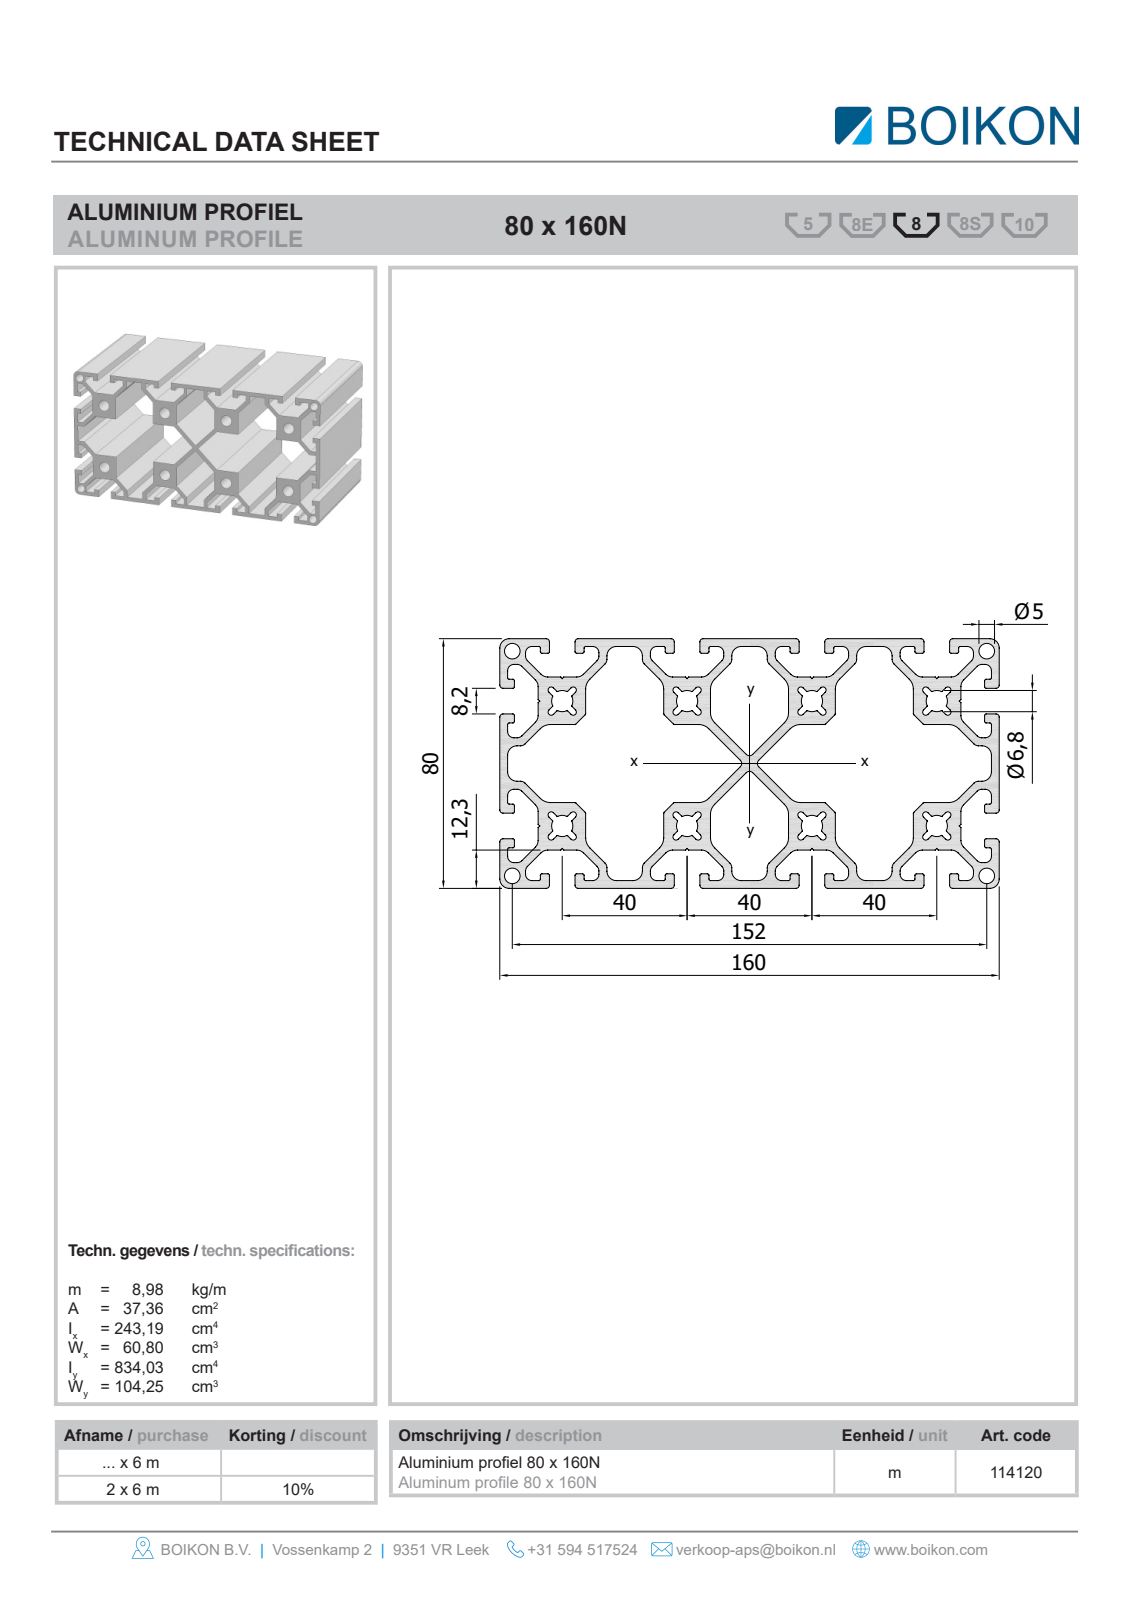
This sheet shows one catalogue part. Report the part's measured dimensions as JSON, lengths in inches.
{"part_name": "Root; 11412080x160NBOIKON0", "step_written_by": "HiCAD 2013 1802.4 Build 509 (AUTOMOTIVE_DESIGN)", "units": "inches", "bodies": {"solids": 1, "faces": 258, "planar": 242, "cylindrical": 16, "other": 0}, "overall_size": [39.37, 6.299, 3.15], "volume_in3": 207, "surface_area_in2": 3331, "round_holes": [[0.268, 8], [0.197, 4]], "partial_cylinders_radius": [[0.118, 4]], "face_to_face_distances": [0.094, 1.113, 1.575, 3.15, 2.227, 0.606, 1.091, 0.996, 2.059, 1.965], "hole_center_spacings": [1.575, 2.293, 2.227, 0.891, 3.118, 3.15, 3.521, 3.831]}
